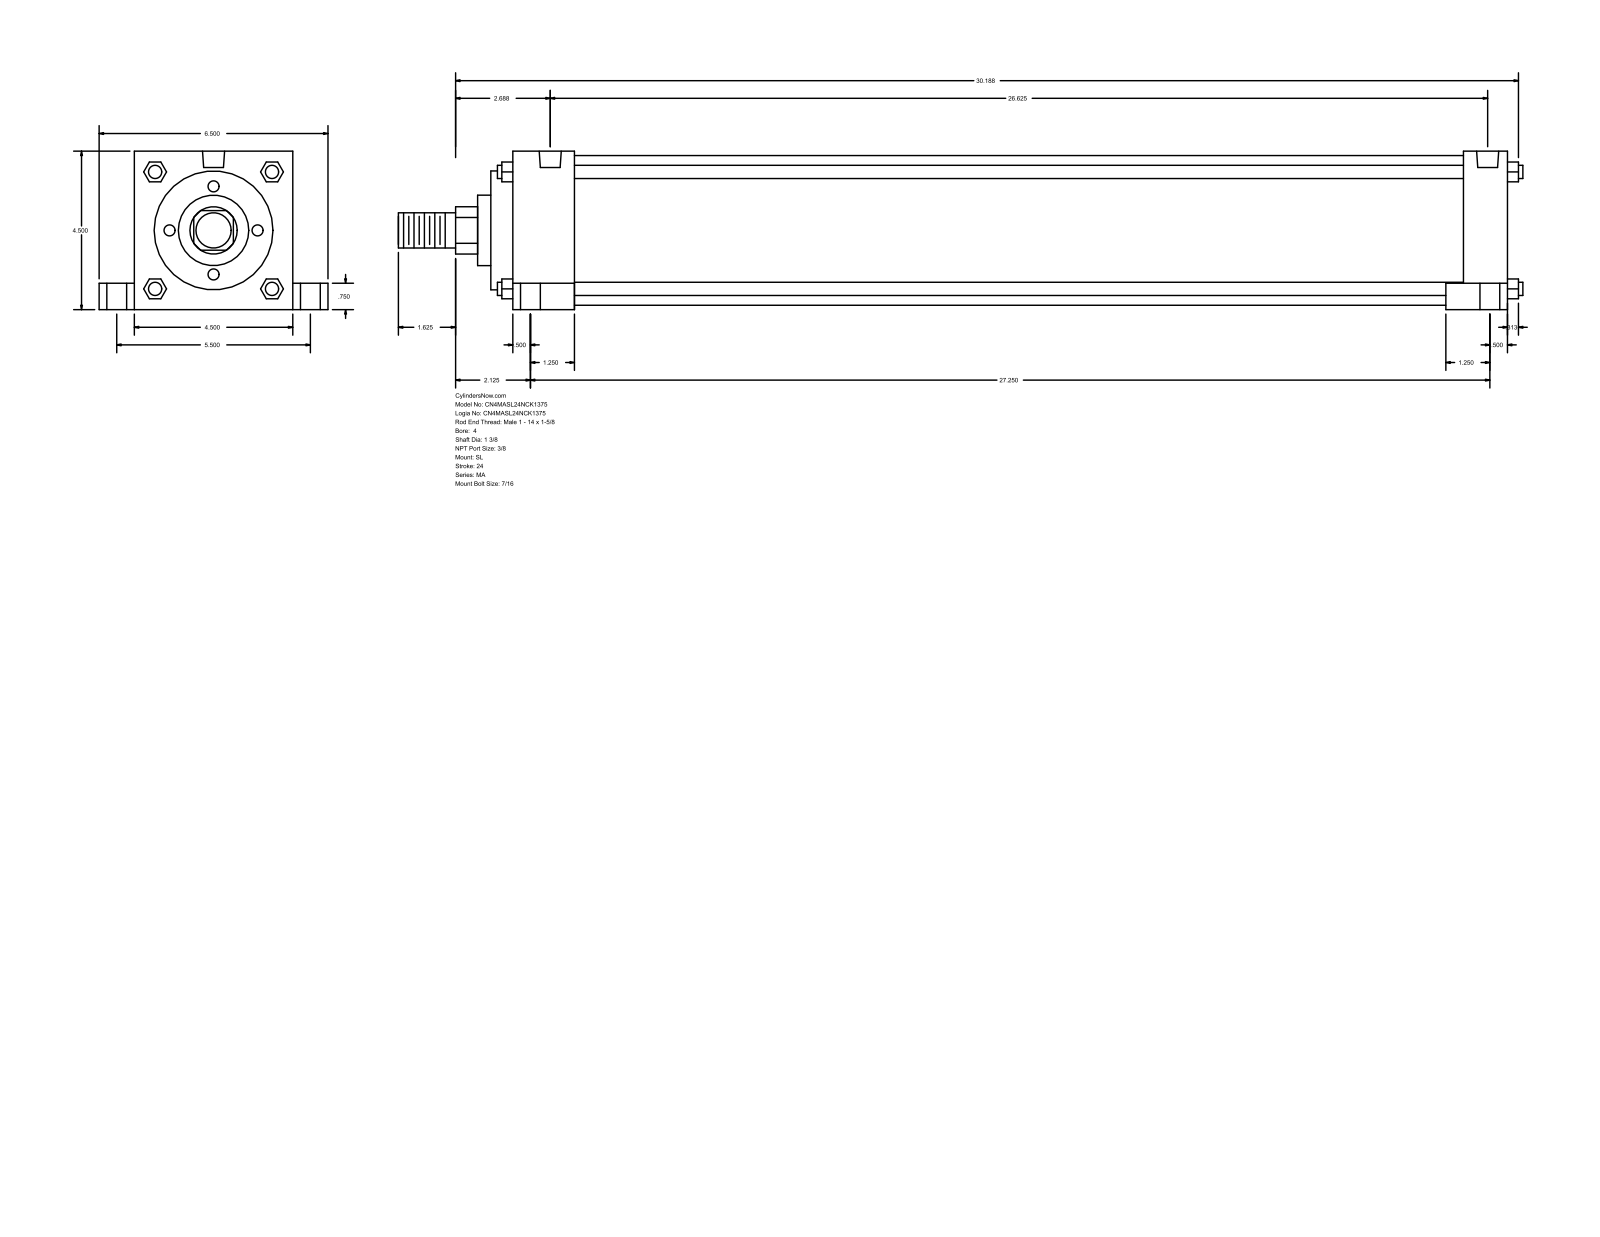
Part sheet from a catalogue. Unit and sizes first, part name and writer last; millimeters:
Units: millimetres
Overall size (bounding box): 811.21 × 165.1 × 114.3
Round holes (diameter × count): ⌀11.11 ×4, ⌀14.29 ×4, ⌀20.64 ×4, ⌀15.93 ×2
Round bosses / shafts (diameter × count): ⌀9.53 ×4, ⌀107.95 ×1, ⌀85.72 ×1, ⌀50.8 ×1, ⌀34.92 ×1, ⌀25.4 ×1
Partial cylindrical surfaces — rounded edges, fillets, slot ends (radius × count): R17.06 ×1
Main face-to-face distances: 114.3, 717.56, 15.87, 733.43, 60.32, 44.45, 673.11, 701.68, 685.81, 641.36
Hole centre spacings: 4.77, 69.87, 70.14, 71.29, 72.4, 139.7, 666.74, 671.51
Bodies: 0 solids, 150 faces (113 planar, 37 cylindrical, 0 other)
Part name (STEP PRODUCT): MA_SL__0400_1.375
STEP written by: GSSL Pune (CONFIG_CONTROL_DESIGN)
